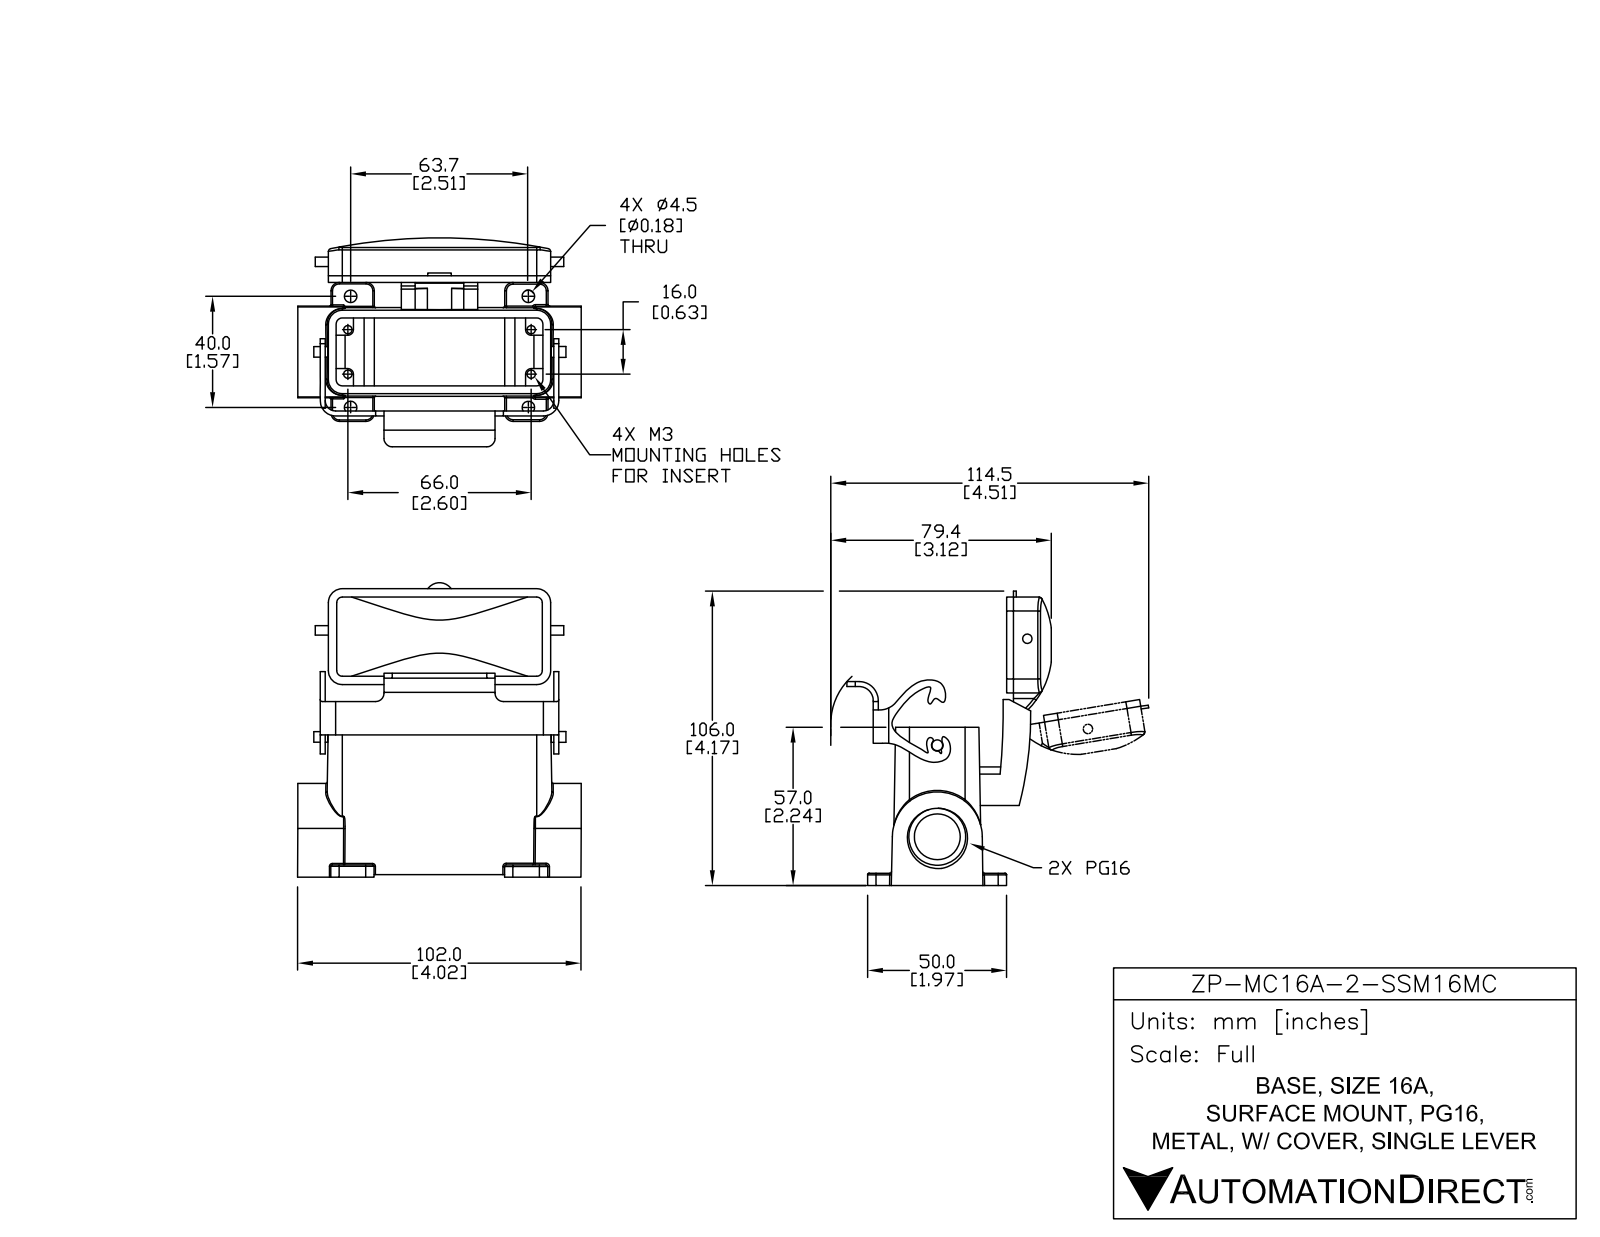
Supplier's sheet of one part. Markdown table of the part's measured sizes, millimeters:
| quantity | value |
| --- | --- |
| part name | ZP-MC16A-2-SSM16MC |
| STEP written by | SolidWorks 2014 (AUTOMOTIVE_DESIGN) |
| units | millimeters |
| bodies | 7 solids, 420 faces (161 planar, 177 cylindrical, 82 other) |
| overall size | 102 × 101.44 × 75.2 |
| volume | 91 614 mm³ |
| surface area | 57 078 mm² |
| round holes (diameter × count) | 3 × 4, 4.5 × 4, 16.5 × 1, 20.5 × 1 |
| round bosses / shafts (diameter × count) | 7.5 × 1, 3.9 × 1, 3.8 × 1, 3.38 × 1 |
| partial cylindrical surfaces (radius × count) | 0.5 × 18, 0.6 × 13, 3 × 12, 2 × 10, 5 × 8, 1 × 4, 3.75 × 2, 5.55 × 2 |
| main face-to-face distances | 2.77, 3, 4.44, 0.52, 1.8, 94.83, 0.92, 3.52, 1.44, 67.83 |
| hole center spacings | 12.04, 28.02, 66.1, 70.77, 16, 40, 64, 66 |
